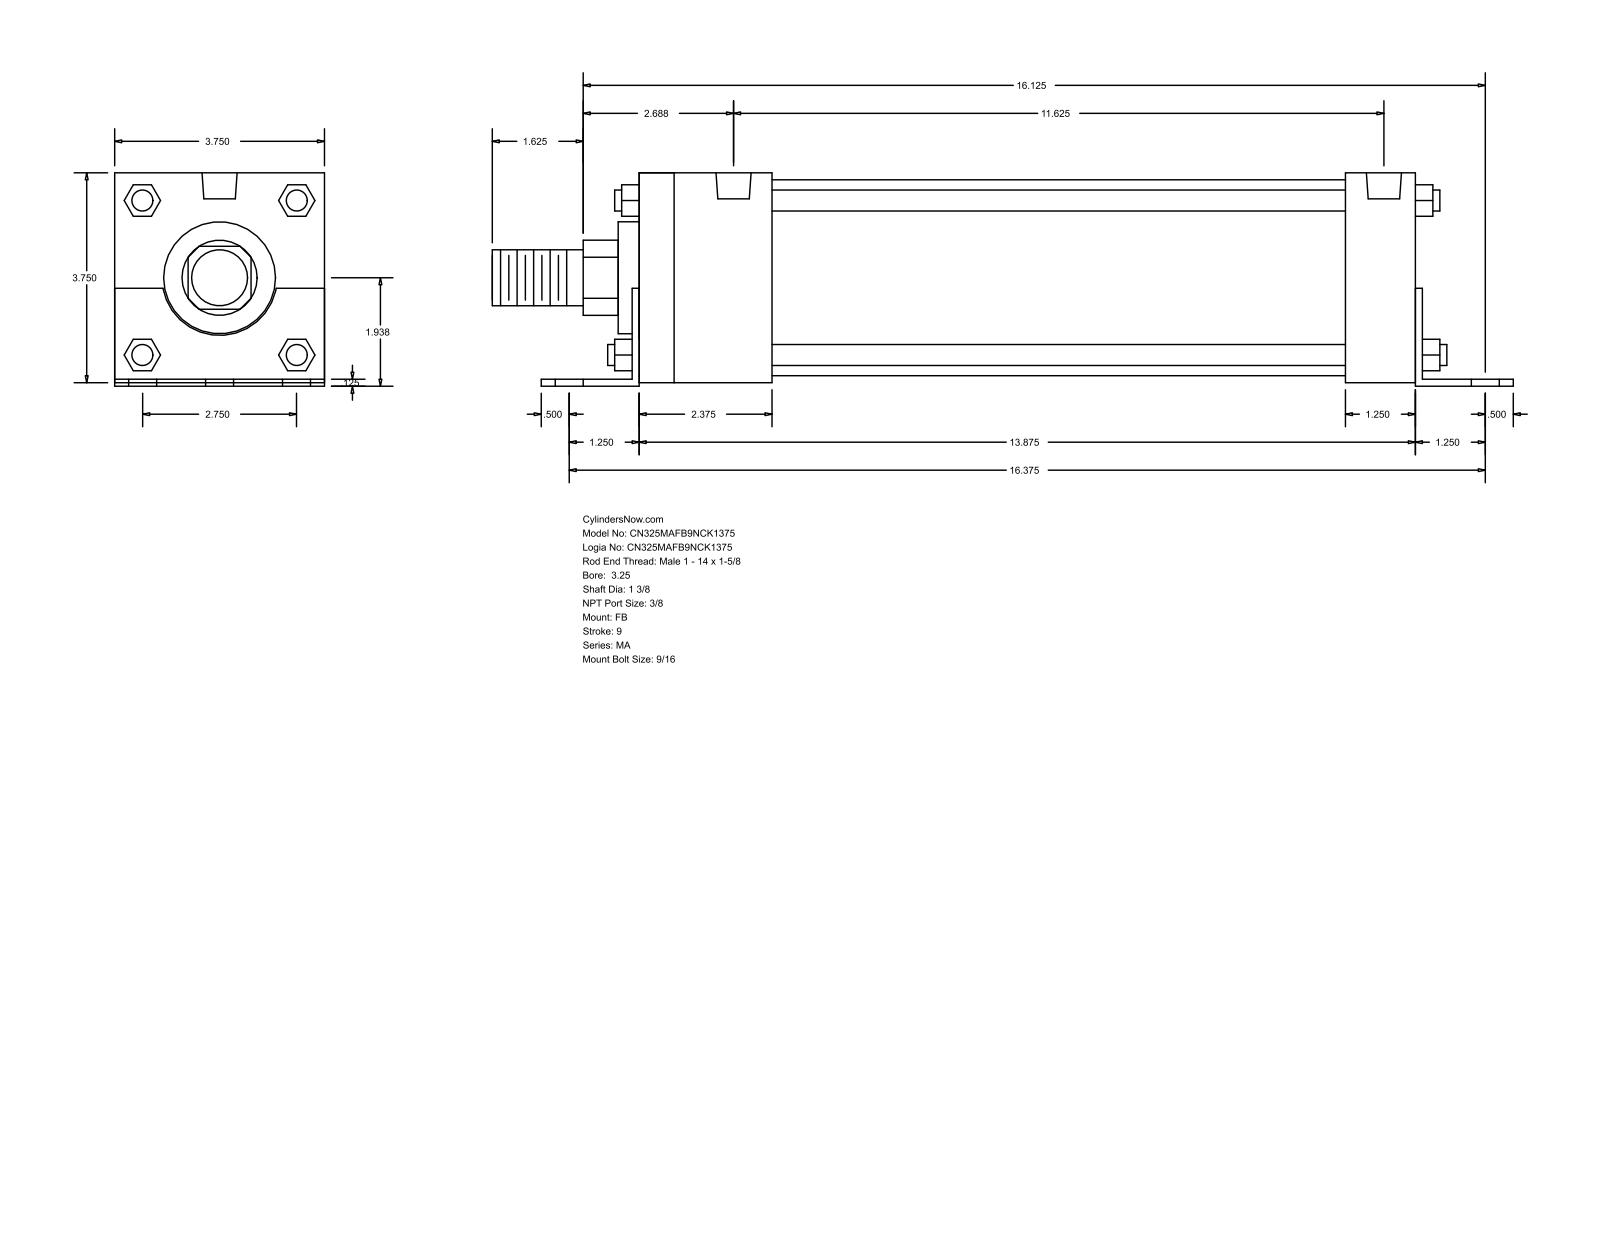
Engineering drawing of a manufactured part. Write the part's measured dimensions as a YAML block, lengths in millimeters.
part_name: "MA_FB__0325_1.375"
step_written_by: "GSSL Pune (CONFIG_CONTROL_DESIGN)"
units: millimeters
bodies: {solids: 0, faces: 140, planar: 105, cylindrical: 35, other: 0}
overall_size: [463.55, 96.84, 95.25]
round_holes:
  - {diameter: 14.29, count: 6}
  - {diameter: 11.11, count: 4}
  - {diameter: 15.93, count: 2}
round_bosses_or_shafts:
  - {diameter: 9.53, count: 4}
  - {diameter: 88.9, count: 1}
  - {diameter: 50.8, count: 1}
  - {diameter: 34.92, count: 1}
  - {diameter: 25.4, count: 1}
partial_cylinders:
  - {radius: 17.06, count: 1}
  - {radius: 26.16, count: 1}
face_to_face_distances: [95.24, 3.17, 1.59, 96.83, 1.58, 93.66, 3.18, 352.42, 355.6, 31.75]
hole_center_spacings: [34.92, 417.38, 415.92, 4.77, 57.78, 61.64, 69.84, 82.38]
